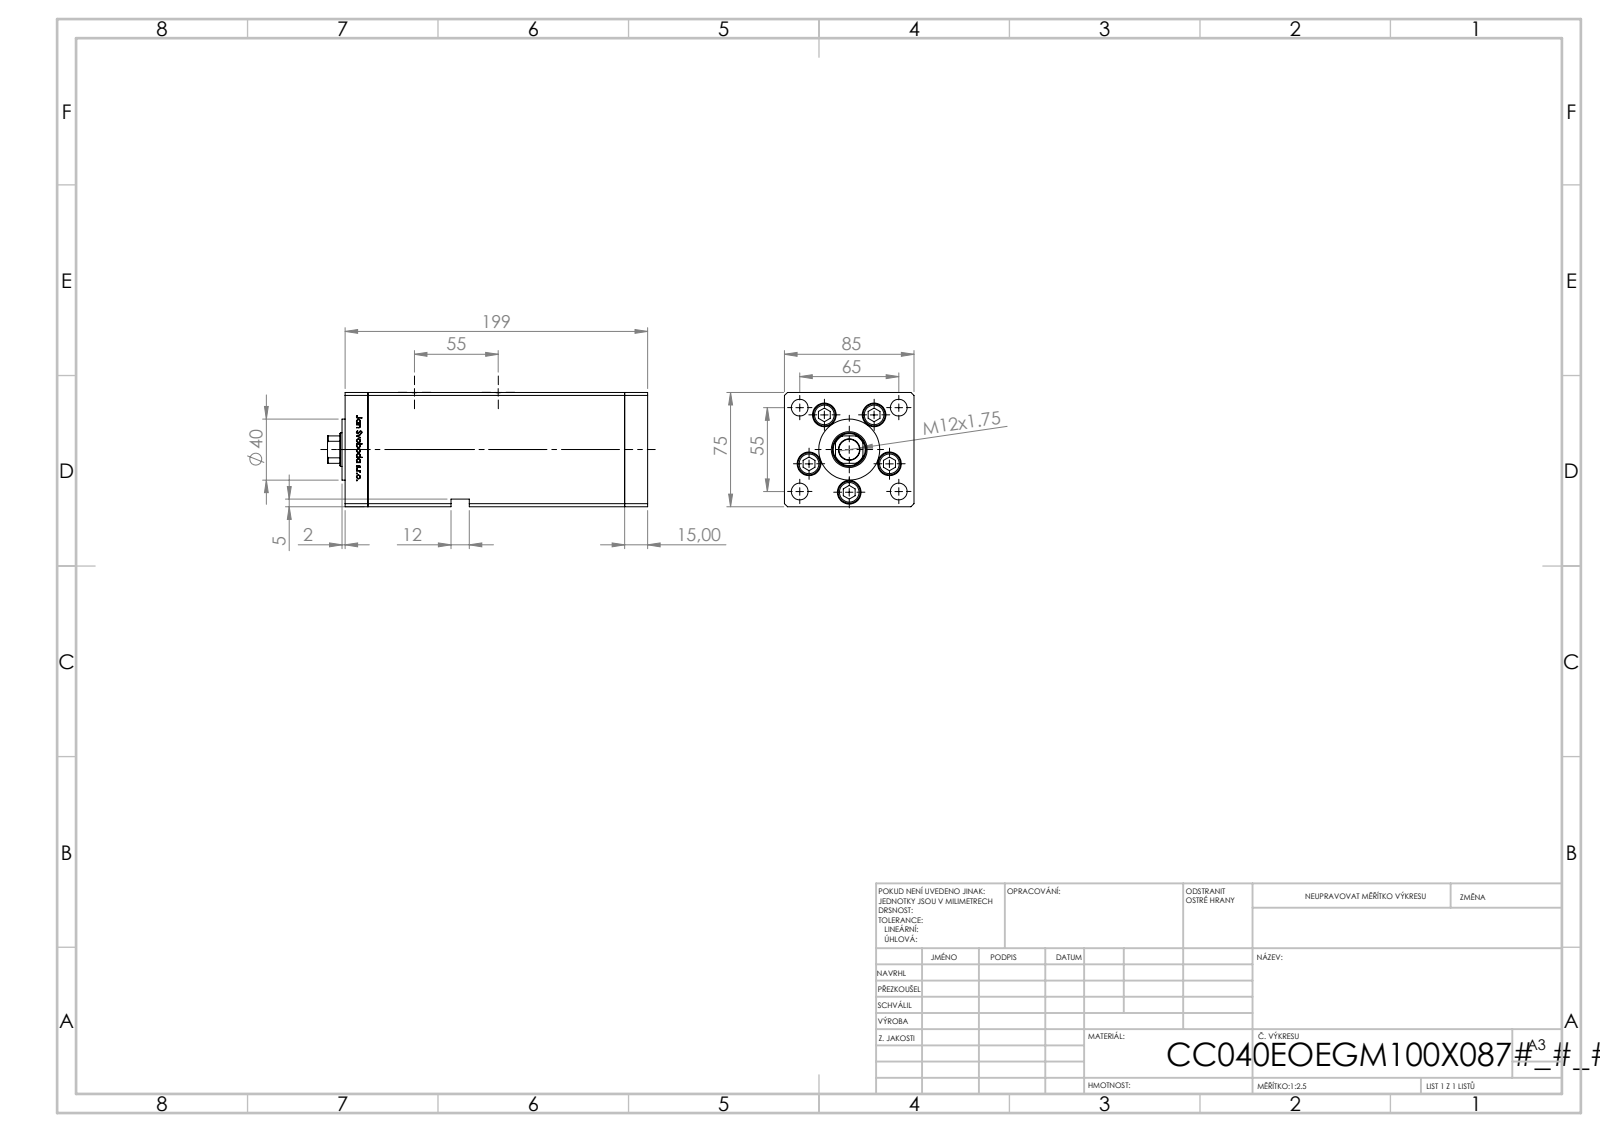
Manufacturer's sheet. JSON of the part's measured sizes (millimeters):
{"part_name": "V220C BACK_E; V220C_FRONT_E; ALLEN BOLT; V220C_VC_E (+1 more)", "step_written_by": "SolidWorks 2019 (CONFIG_CONTROL_DESIGN)", "units": "millimeters", "bodies": {"solids": 14, "faces": 1214, "planar": 475, "cylindrical": 165, "other": 574}, "overall_size": [210, 85, 75], "volume_mm3": 1076000, "surface_area_mm2": 182851, "round_holes": [[11, 9], [15.5, 5], [10.5, 4], [16.5, 4], [2, 2], [13.16, 2], [13.5, 1], [22, 1], [23.5, 1]], "round_bosses_or_shafts": [[14.5, 5], [8, 5], [40, 1]], "partial_cylinders_radius": [[0.93, 2], [10.5, 1]], "face_to_face_distances": [85, 75, 15, 168.5, 183.5, 198.5, 34.25, 68.5, 10.5, 19.25], "hole_center_spacings": [28, 42.57, 55, 65, 85.15, 16.86, 19.17, 32.33]}
